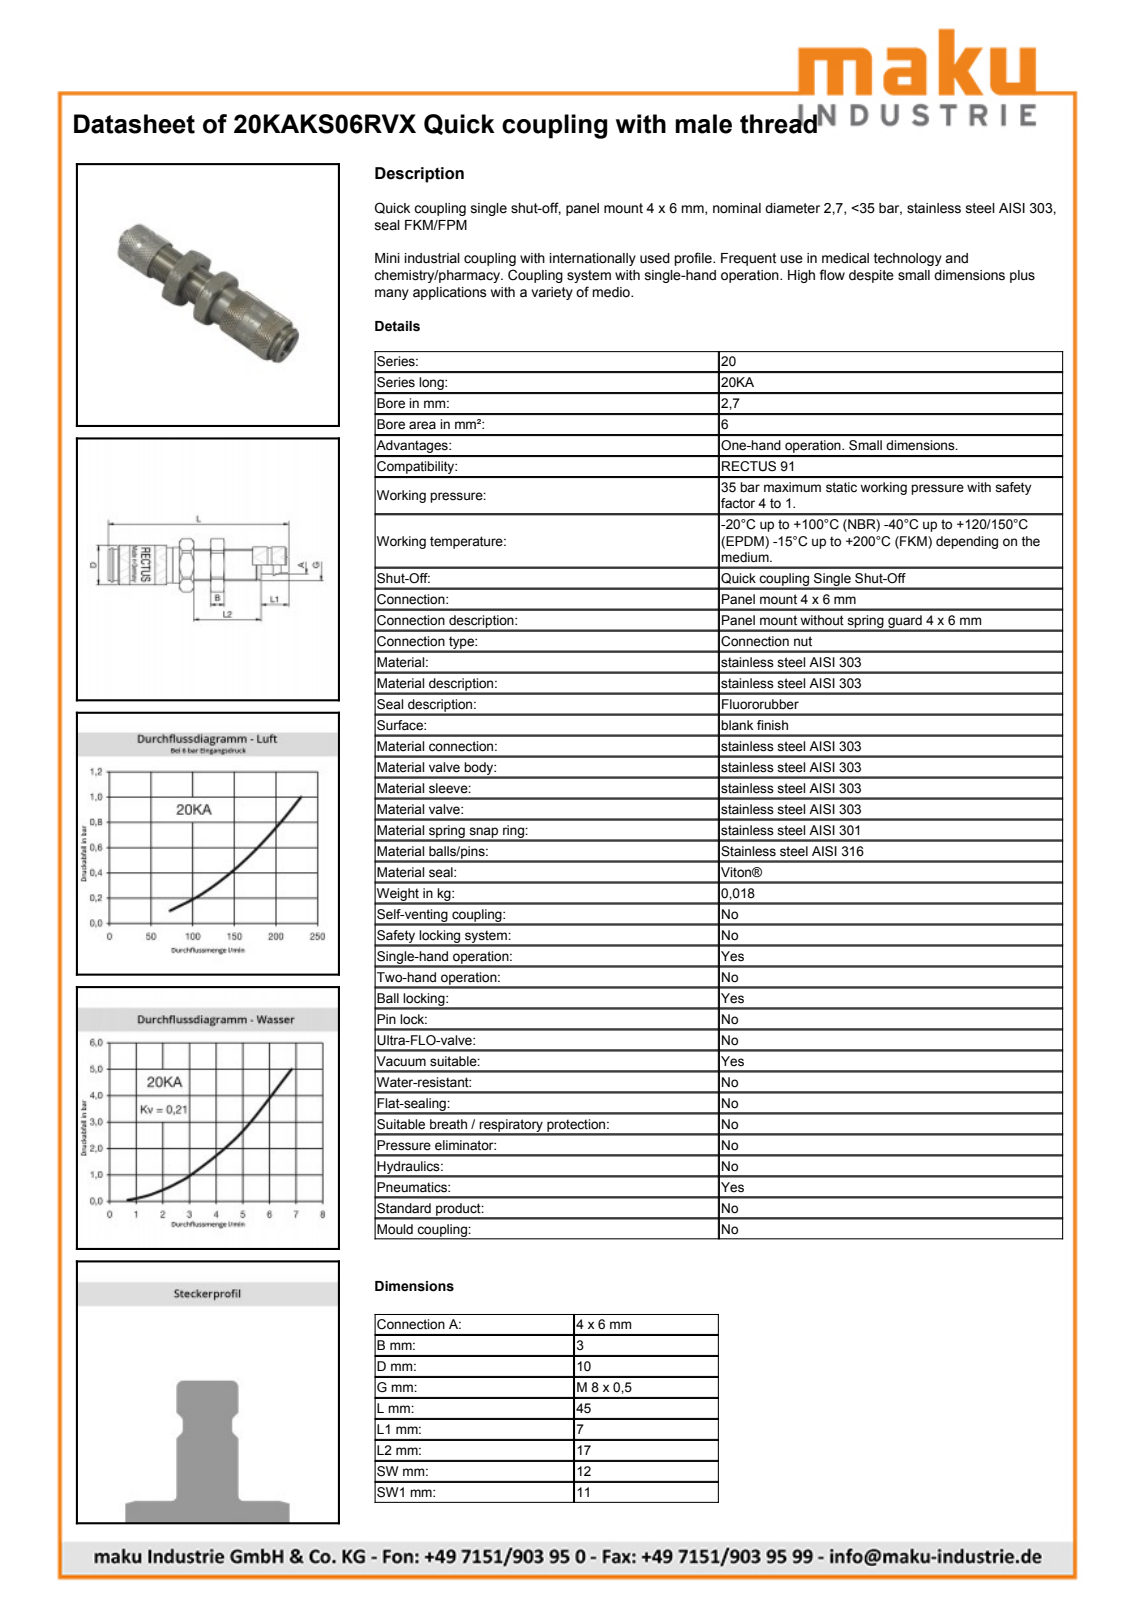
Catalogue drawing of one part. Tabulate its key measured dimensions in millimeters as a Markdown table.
| quantity | value |
| --- | --- |
| part name | D106223 |
| STEP written by | Autodesk Inventor 2011 (AUTOMOTIVE_DESIGN) |
| units | millimeters |
| bodies | 2 solids, 515 faces (174 planar, 85 cylindrical, 256 other) |
| overall size | 45.05 × 13.29 × 13.07 |
| volume | 2 913 mm³ |
| surface area | 3 257 mm² |
| round holes (diameter × count) | 6.25 × 1, 6.3 × 1, 6.45 × 1, 6.5 × 1, 7.46 × 1, 8.1 × 1, 8.15 × 1, 9.15 × 1, 9.2 × 1 |
| round bosses / shafts (diameter × count) | 10.35 × 1, 10 × 1, 9.1 × 1, 9 × 1, 8.9 × 1, 8.7 × 1, 8 × 1, 7.8 × 1 |
| partial cylindrical surfaces (radius × count) | 4.9 × 1, 6.5 × 1, 6.75 × 1 |
| main face-to-face distances | 12, 3.5, 3.05, 11.46, 8.41, 7.96, 4.91, 18, 21.05, 25.96 |
